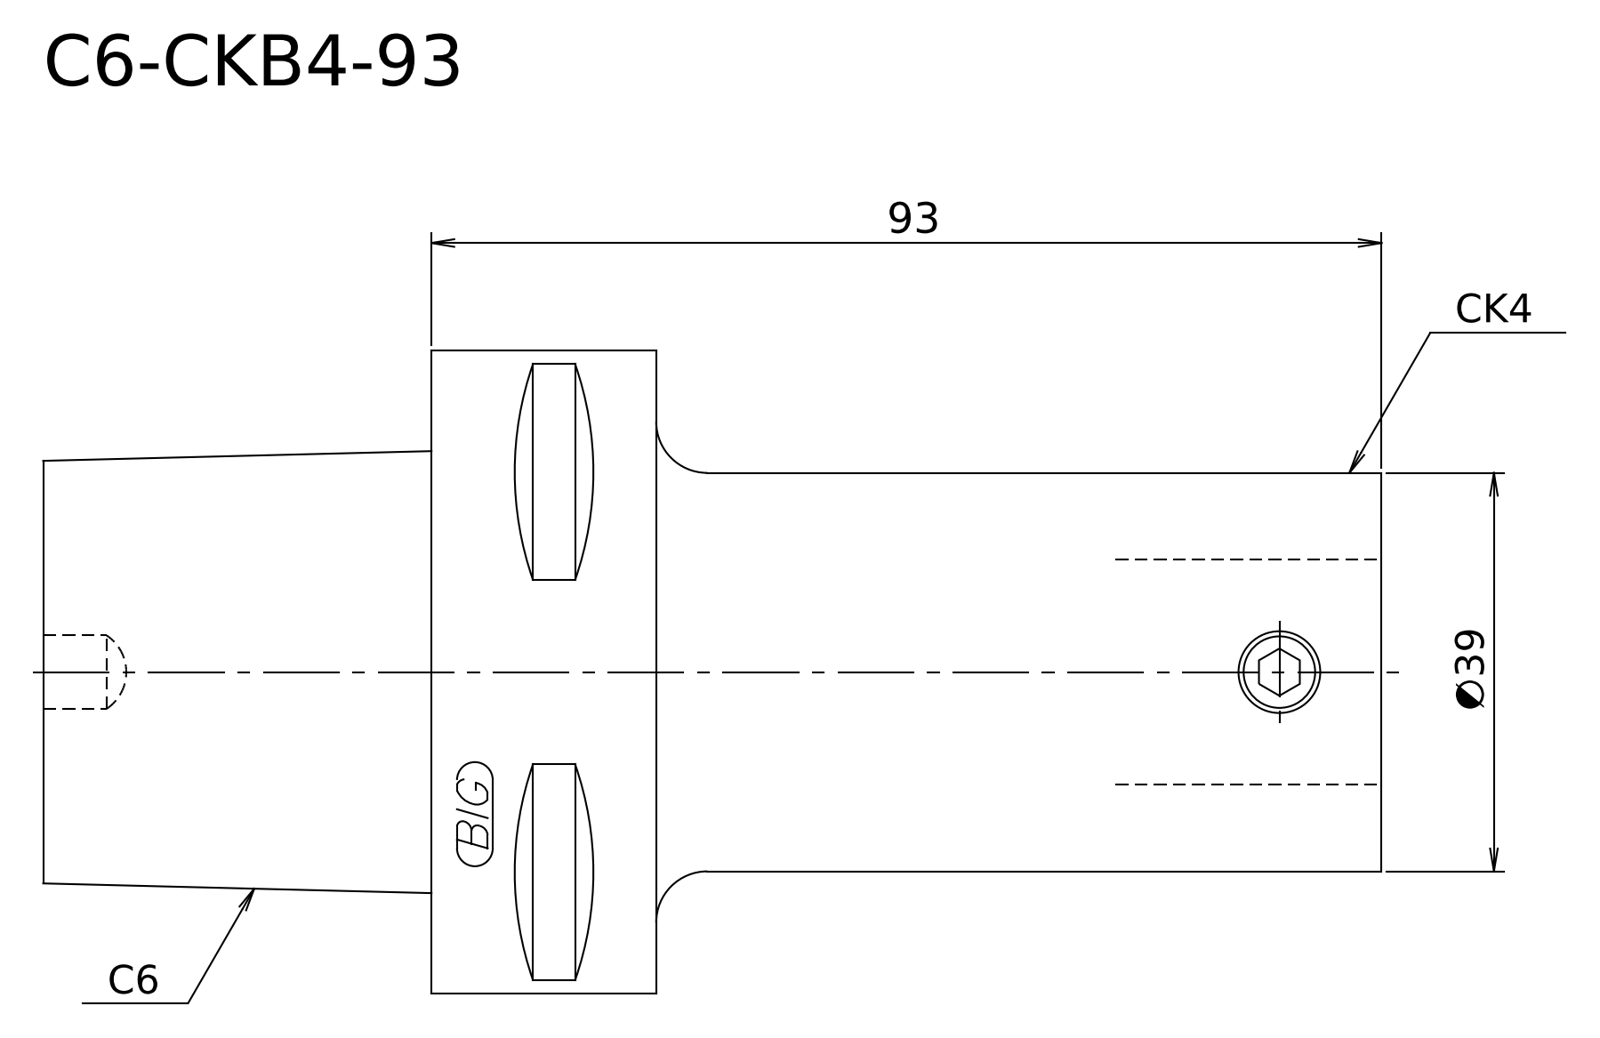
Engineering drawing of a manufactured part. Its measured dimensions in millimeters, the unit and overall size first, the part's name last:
Units: millimetres
Overall size (bounding box): 131 × 62.98 × 62.98
Round bosses / shafts (diameter × count): ⌀62.98 ×1, ⌀39 ×1
Main face-to-face distances: 38, 22, 60, 71, 93, 131
Volume: 209 804 mm³ · Surface area: 23 987 mm²
Bodies: 1 solid, 10 faces (4 planar, 2 cylindrical, 4 other)
STEP written by: Kubotek KeyCreator V8.5.1 (14335) (CONFIG_CONTROL_DESIGN)
